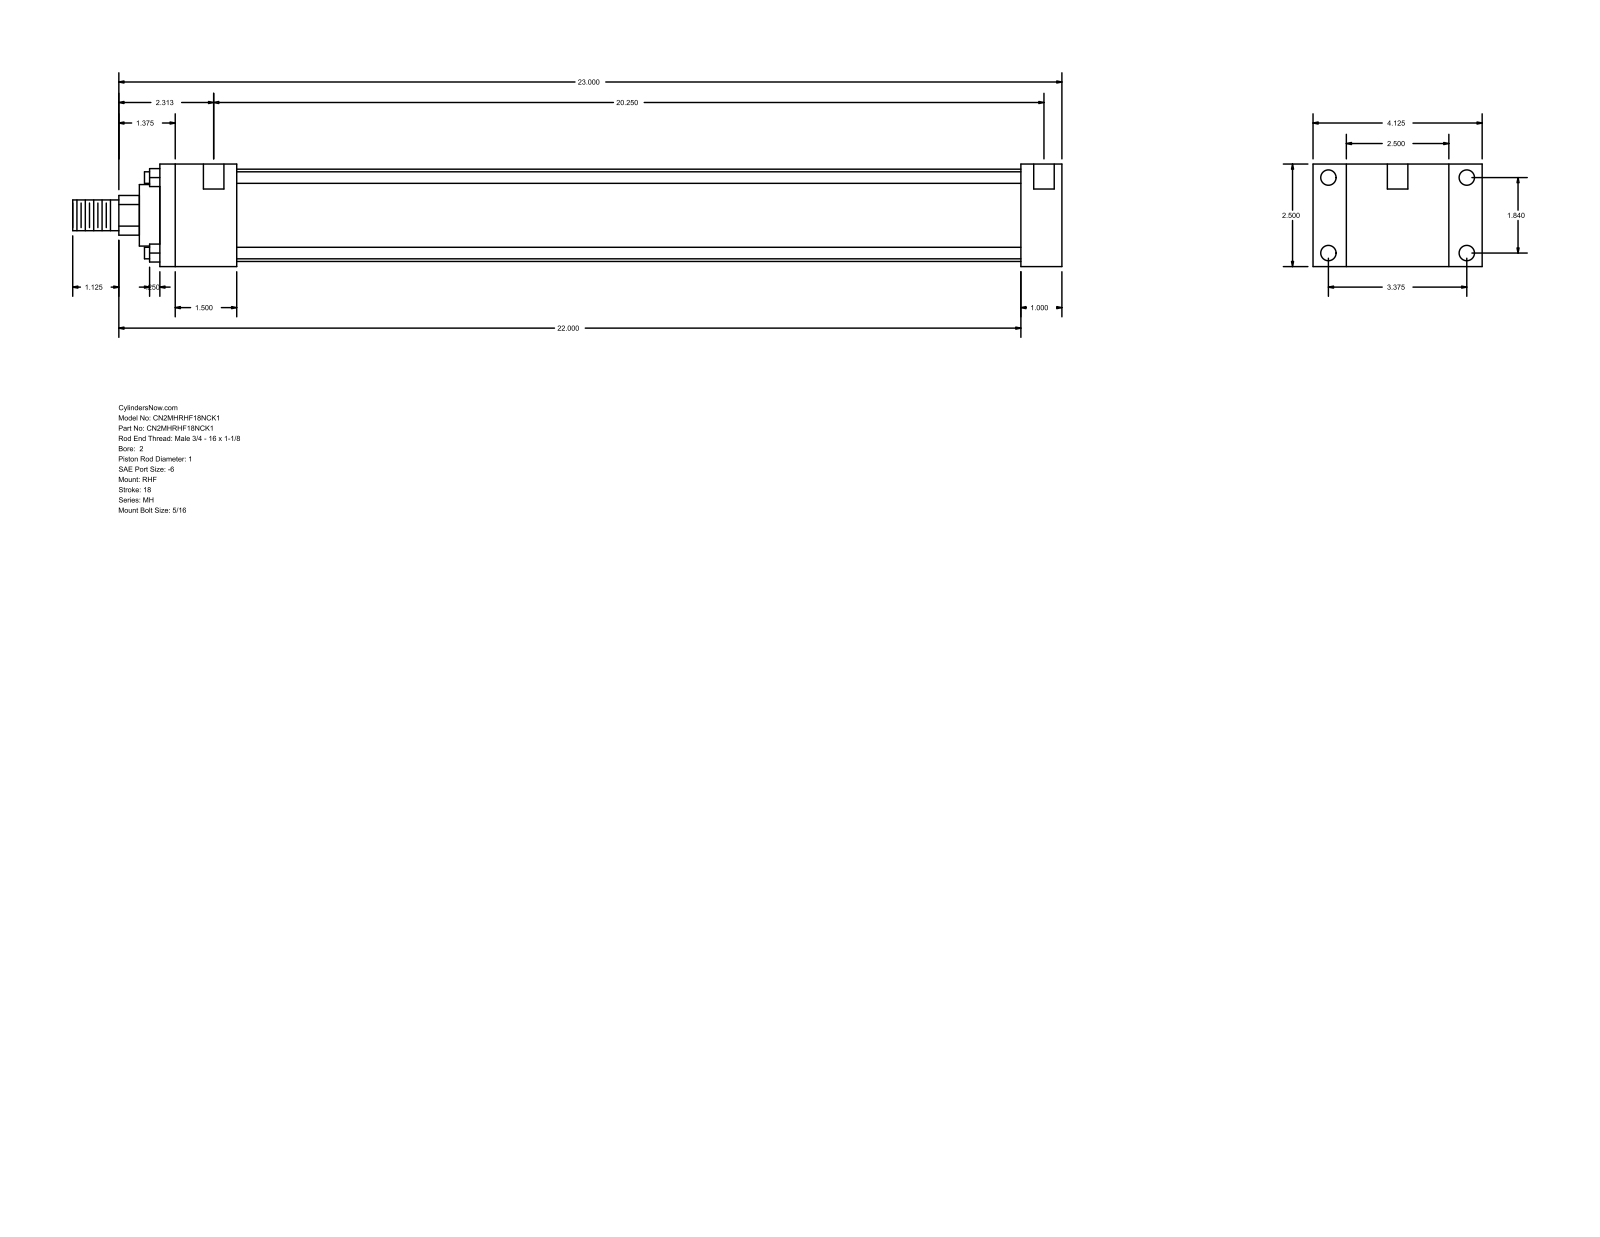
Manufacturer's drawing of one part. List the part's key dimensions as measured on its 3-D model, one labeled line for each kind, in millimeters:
Part name (STEP PRODUCT): MH_RHF__0200_1
STEP written by: GSSL Pune (CONFIG_CONTROL_DESIGN)
Units: millimetres
Bodies: 0 solids, 88 faces (60 planar, 28 cylindrical, 0 other)
Overall size (bounding box): 612.77 × 104.78 × 63.5
Round holes (diameter × count): ⌀5.56 ×4, ⌀9.53 ×4, ⌀12.7 ×2
Round bosses / shafts (diameter × count): ⌀7.14 ×4, ⌀57.15 ×1, ⌀38.1 ×1, ⌀25.4 ×1, ⌀19.05 ×1
Partial cylindrical surfaces — rounded edges, fillets, slot ends (radius × count): R12.29 ×1
Main face-to-face distances: 63.5, 25.4, 20.64, 84.14, 558.8, 533.4, 104.78, 47.63, 485.77, 511.17
Hole centre spacings: 46.74, 85.72, 97.63, 522.28, 3.17, 4.76, 514.35, 517.52
